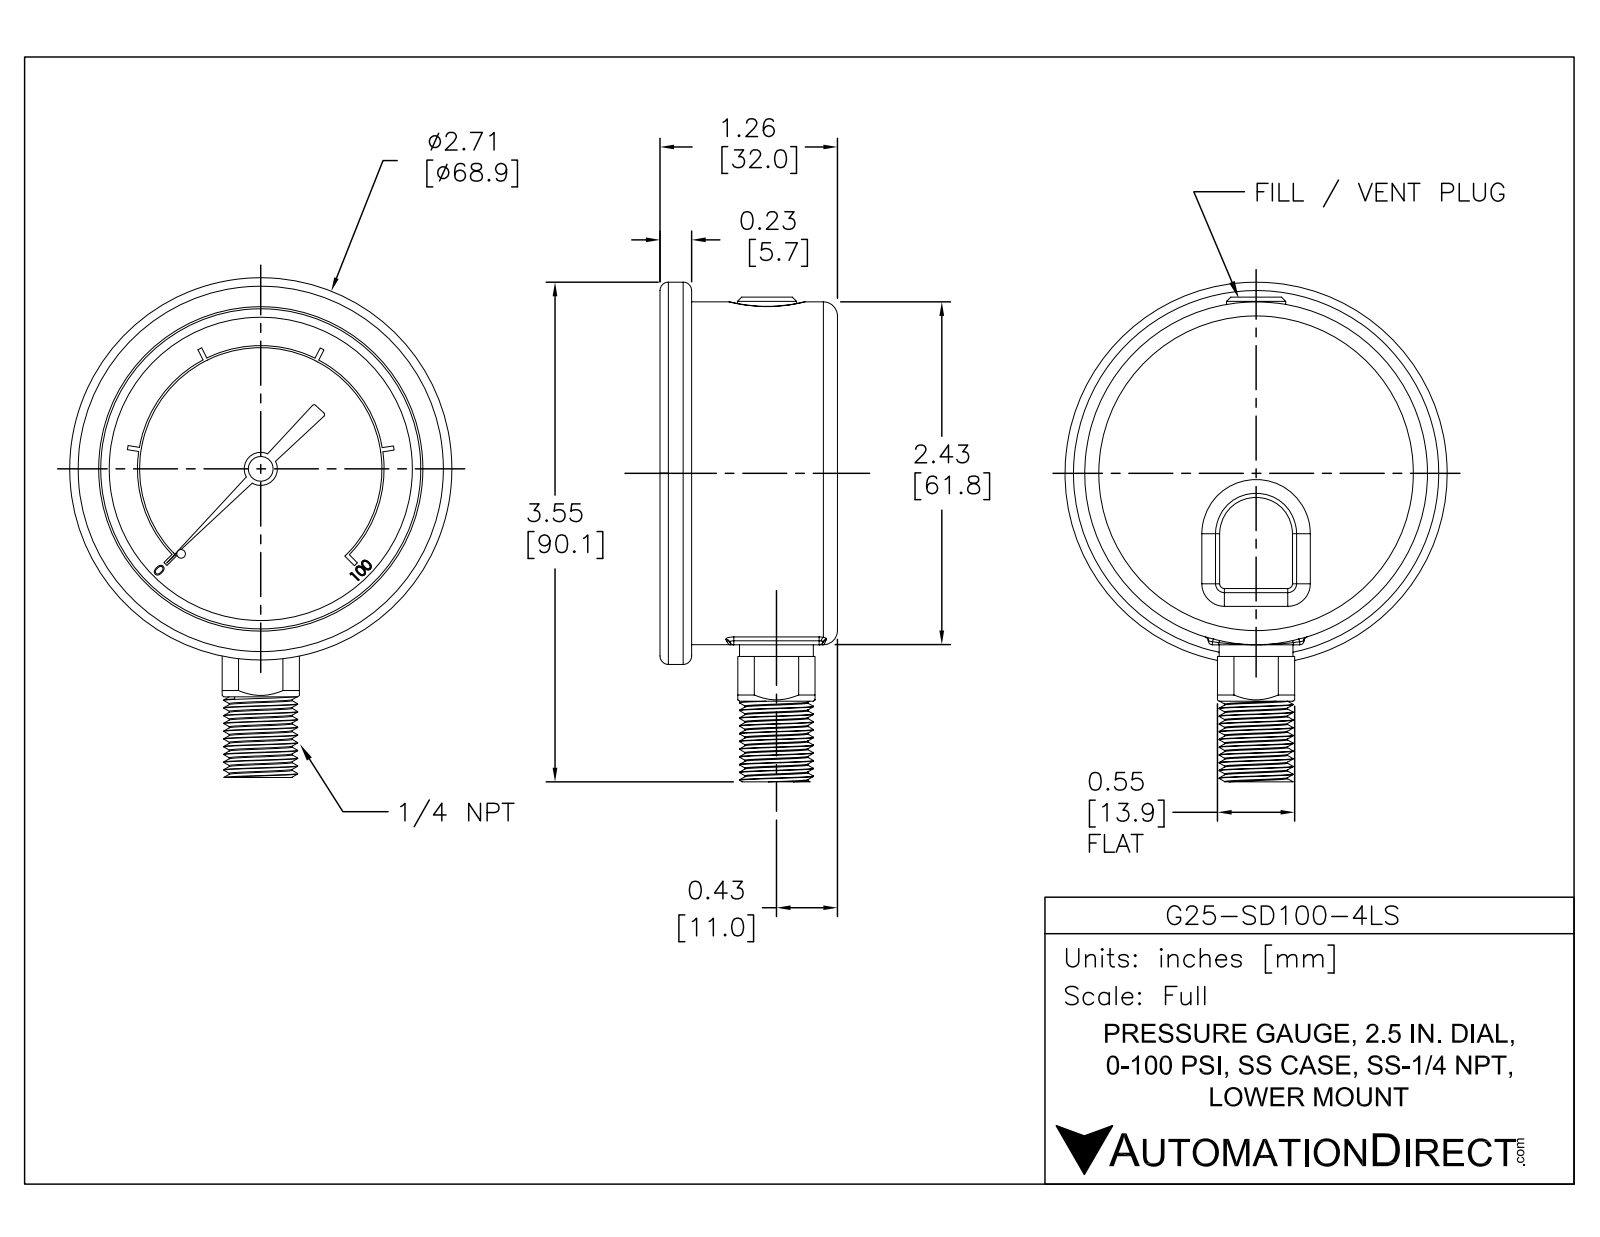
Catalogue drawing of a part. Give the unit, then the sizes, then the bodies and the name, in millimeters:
Units: millimetres
Overall size (bounding box): 90.1 × 68.9 × 32
Round holes (diameter × count): ⌀0.7 ×1, ⌀1.8 ×1, ⌀3 ×1, ⌀57.7 ×1
Round bosses / shafts (diameter × count): ⌀68.9 ×1, ⌀61.8 ×1, ⌀13.3 ×1, ⌀10.7 ×1, ⌀6 ×1, ⌀4.5 ×1, ⌀3.6 ×1, ⌀1 ×1
Partial cylindrical surfaces — rounded edges, fillets, slot ends (radius × count): R0.8 ×9, R2.5 ×3, R0.4 ×2, R8 ×1, R21.8 ×1, R22.2 ×1
Main face-to-face distances: 25.7, 32, 6.4, 26.3, 0.6, 5.7, 2.5, 23.1, 23.7, 29.5
Hole centre spacings: 1.7
Volume: 86 410 mm³ · Surface area: 15 920 mm²
Bodies: 1 solid, 343 faces (195 planar, 85 cylindrical, 63 other)
Part name (STEP PRODUCT): G25-SD100-4LS
STEP written by: SolidWorks 2021 (AUTOMOTIVE_DESIGN)
